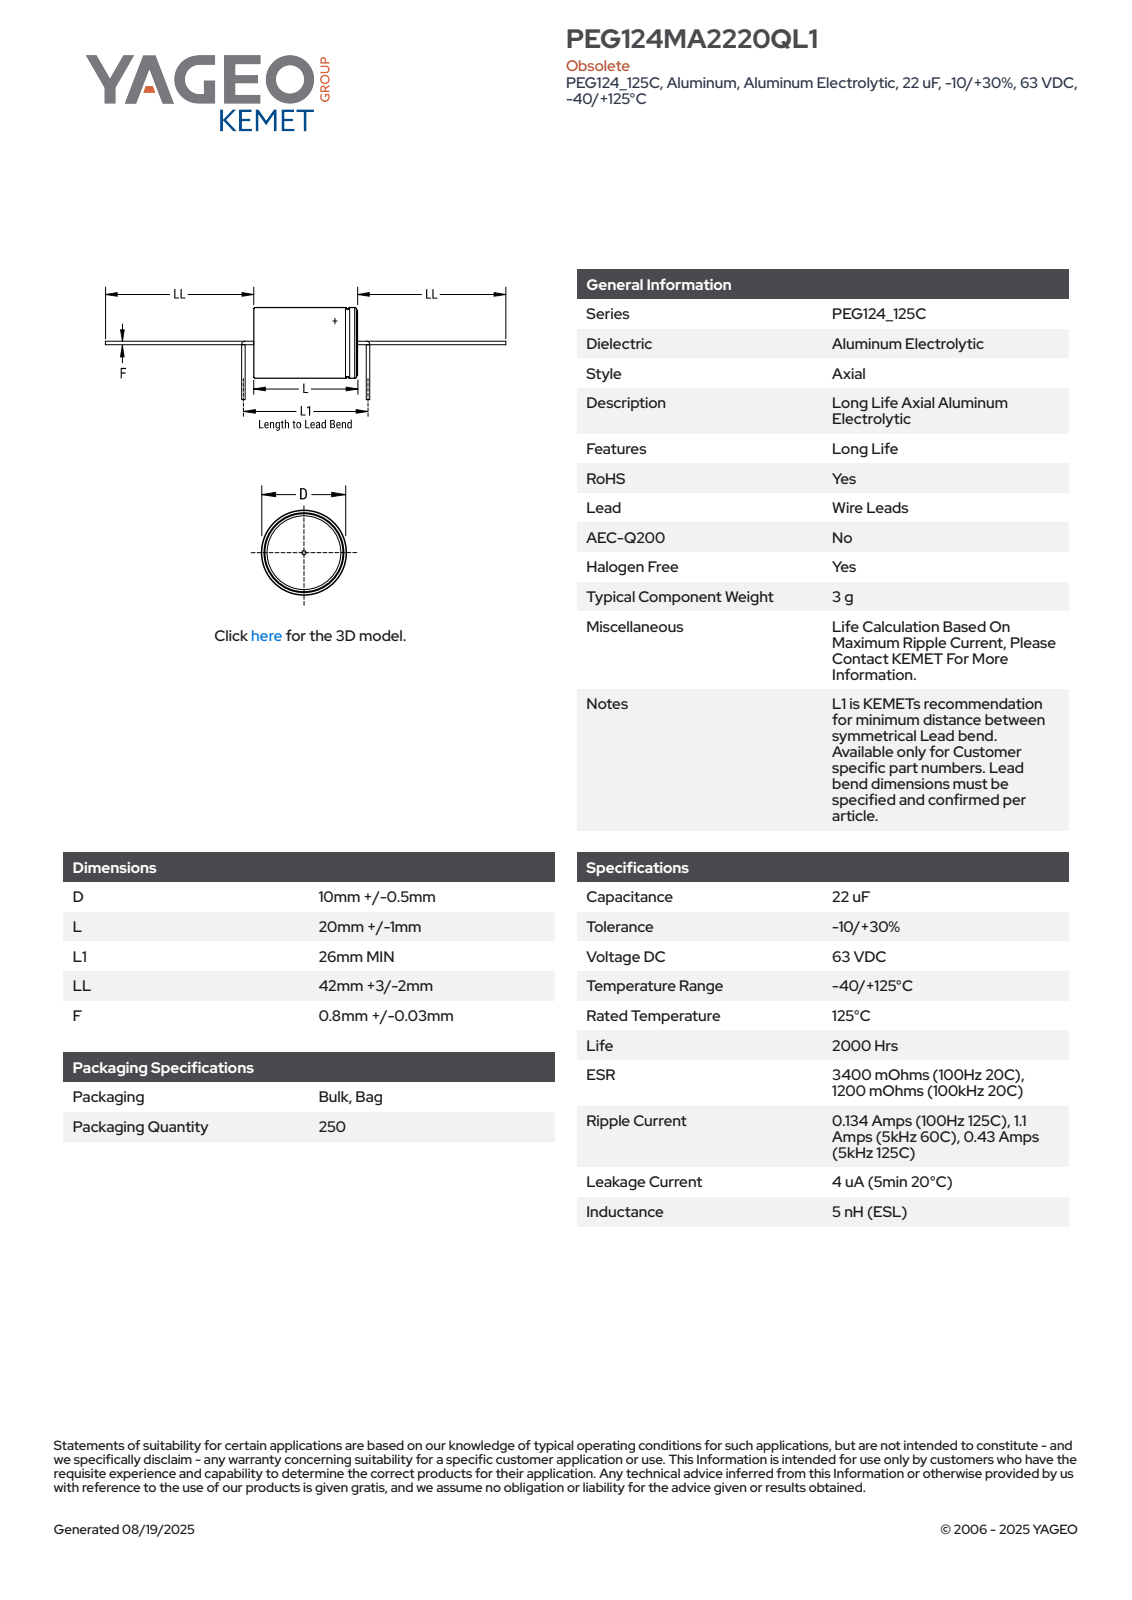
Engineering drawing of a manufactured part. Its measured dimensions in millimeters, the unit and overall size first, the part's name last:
Units: millimetres
Overall size (bounding box): 108 × 10.5 × 10.5
Round holes (diameter × count): ⌀9.5 ×1
Round bosses / shafts (diameter × count): ⌀10.5 ×1, ⌀10 ×1, ⌀0.83 ×1
Partial cylindrical surfaces — rounded edges, fillets, slot ends (radius × count): R5.24 ×1
Main face-to-face distances: 20, 21, 1, 45, 65, 66, 108, 63, 43, 42
Volume: 1 790 mm³ · Surface area: 1 127 mm²
Bodies: 1 solid, 99 faces (27 planar, 29 cylindrical, 43 other)
Part name (STEP PRODUCT): CAA_PEG124_10X20_D10.5L21LL45F0.83
STEP written by: SolidWorks 2014 (AUTOMOTIVE_DESIGN)
